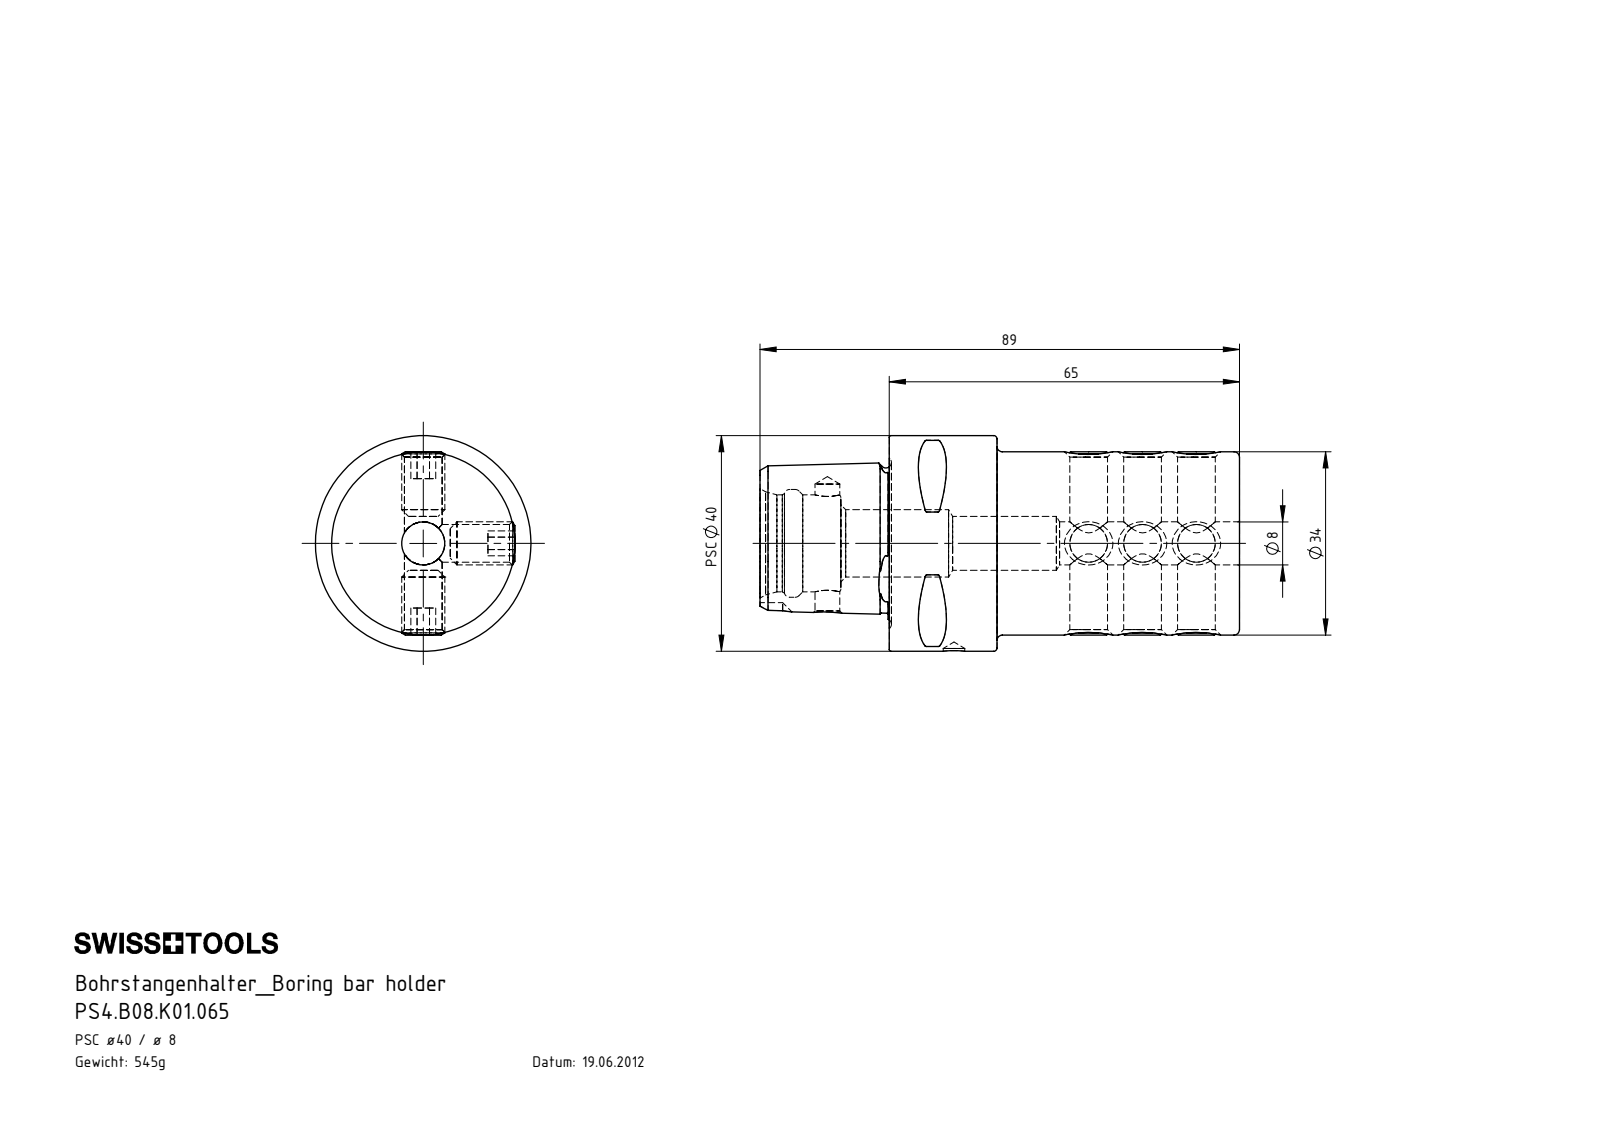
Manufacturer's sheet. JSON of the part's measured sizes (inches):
{"part_name": "PS4.B08.K01.065; ISO 4026 - M8 x 12_PreviewCfg; PS4-B08.K01.065_A", "step_written_by": "SolidWorks 2017 (AUTOMOTIVE_DESIGN)", "units": "inches", "bodies": {"solids": 10, "faces": 224, "planar": 101, "cylindrical": 38, "other": 85}, "overall_size": [3.504, 1.575, 1.575], "volume_in3": 4.235, "surface_area_in2": 32.14, "round_holes": [[0.276, 6], [0.157, 1], [0.181, 1], [0.315, 1], [0.394, 1], [0.492, 1], [0.709, 1], [0.787, 1]], "round_bosses_or_shafts": [[0.315, 6], [1.575, 1], [1.339, 1]], "partial_cylinders_radius": [[0.012, 8], [0.118, 1]], "face_to_face_distances": [2.559, 0.197, 0.394, 0.157, 0.787, 0.945, 0.354, 1.772, 1.732, 0.472], "hole_center_spacings": [0.394, 0.787, 0.925, 0.984, 1.378, 1.772, 1.909, 2.303]}
